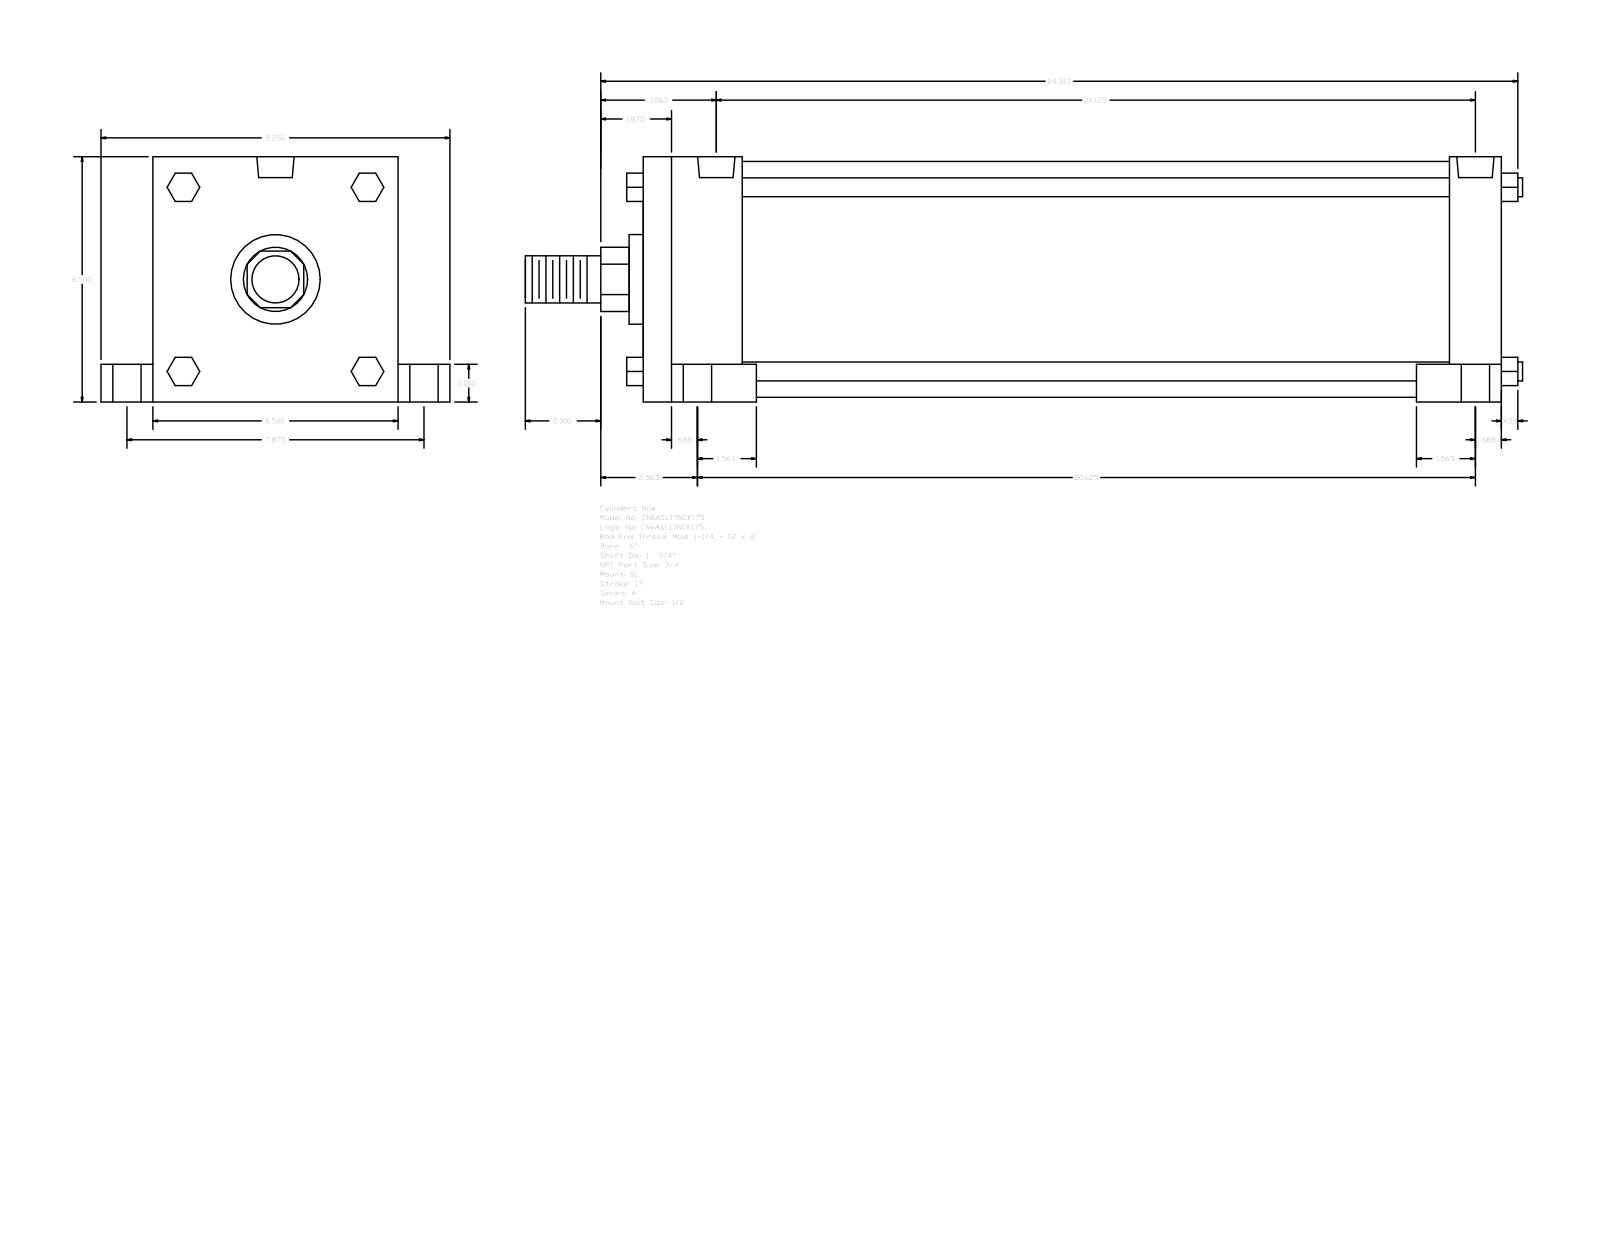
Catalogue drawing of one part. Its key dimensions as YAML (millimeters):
part_name: "A_SL__0600_1.75"
step_written_by: "GSSL Pune (CONFIG_CONTROL_DESIGN)"
units: millimeters
bodies: {solids: 0, faces: 150, planar: 114, cylindrical: 36, other: 0}
overall_size: [671.51, 234.95, 165.1]
round_holes:
  - {diameter: 15.08, count: 4}
  - {diameter: 19.05, count: 4}
  - {diameter: 25.4, count: 4}
  - {diameter: 25.12, count: 2}
round_bosses_or_shafts:
  - {diameter: 12.7, count: 4}
  - {diameter: 158.75, count: 1}
  - {diameter: 60.33, count: 1}
  - {diameter: 44.45, count: 1}
  - {diameter: 31.75, count: 1}
partial_cylinders:
  - {radius: 21.63, count: 1}
face_to_face_distances: [165.1, 577.85, 34.92, 66.68, 511.17, 542.93, 476.25, 25.4, 139.7, 200.02]
hole_center_spacings: [5.56, 100.01, 100.16, 100.81, 101.66, 200.02, 500.05, 505.61]
